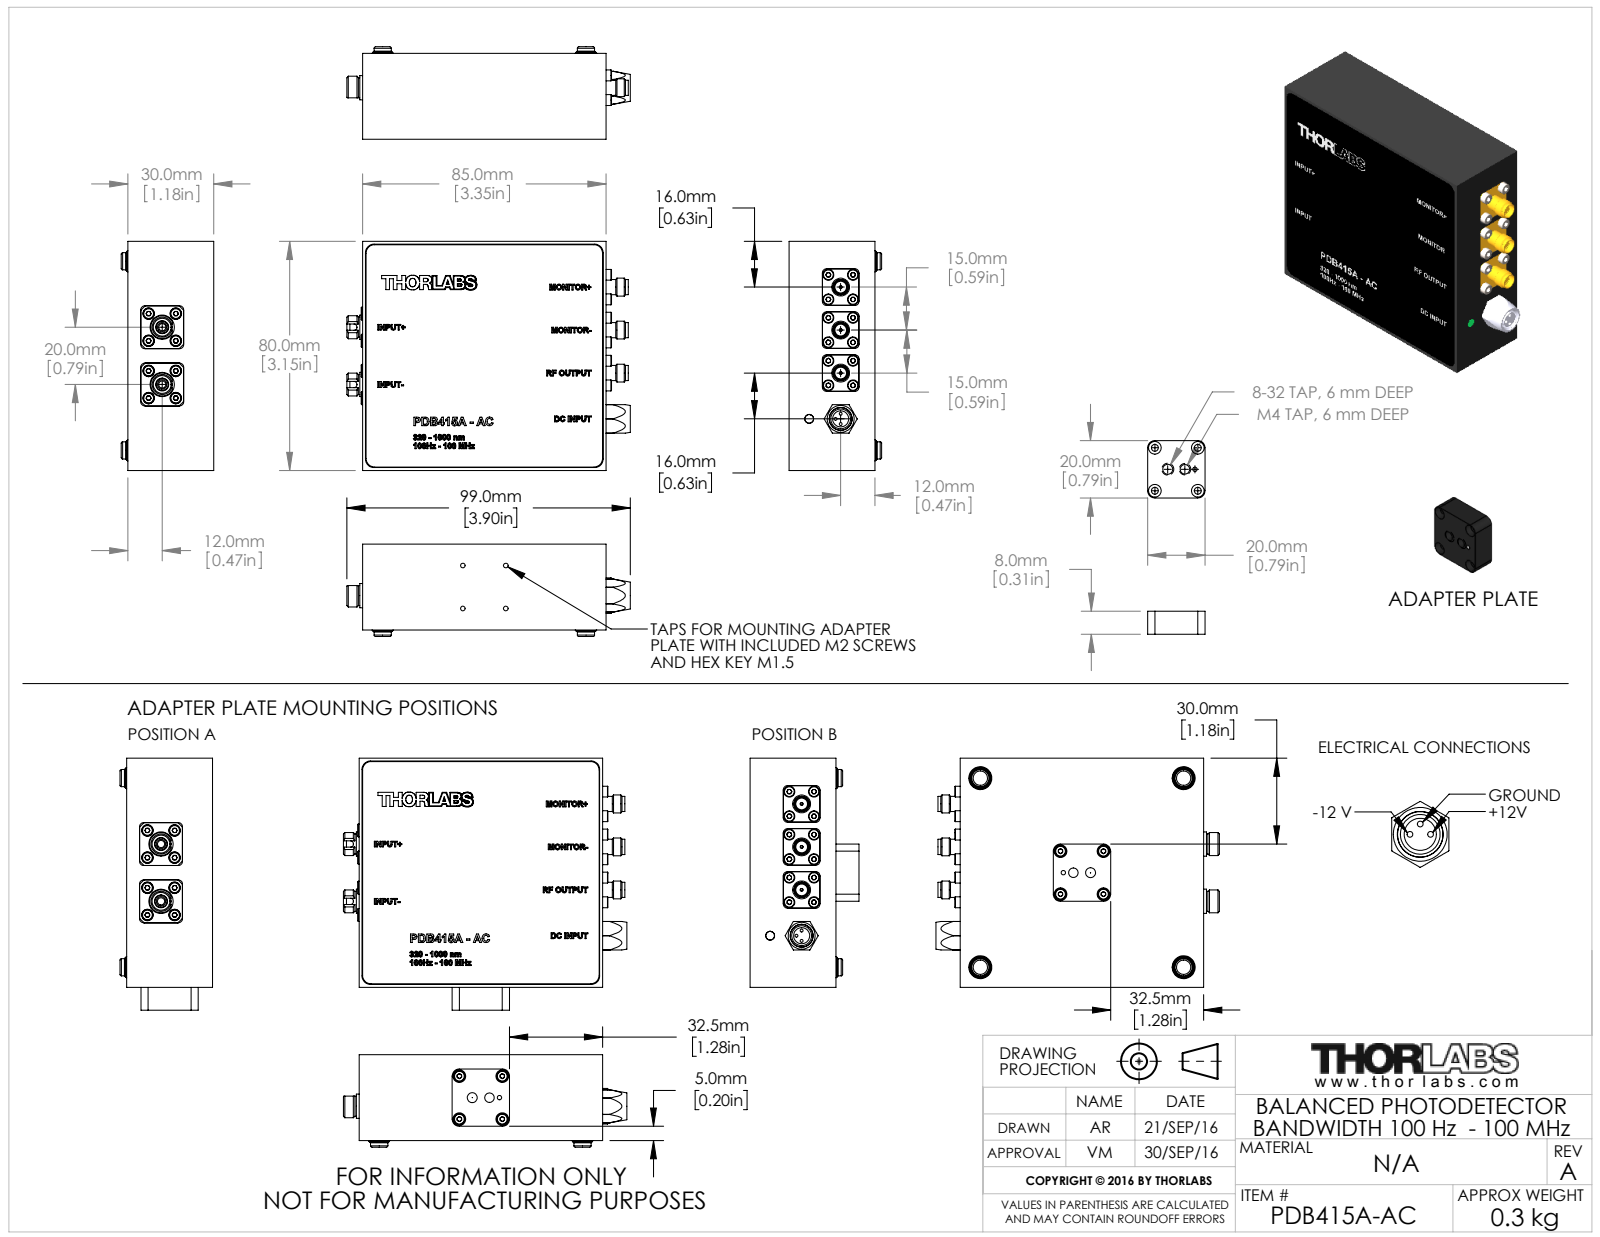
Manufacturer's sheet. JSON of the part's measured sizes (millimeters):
{"part_name": "MTN005470-E0W", "step_written_by": "SolidWorks 2014 (AUTOMOTIVE_DESIGN)", "units": "millimeters", "bodies": {"solids": 90, "faces": 3091, "planar": 1799, "cylindrical": 584, "other": 708}, "overall_size": [99, 88, 38], "volume_mm3": 87719, "surface_area_mm2": 57809, "round_holes": [[1.6, 38], [2.6, 12], [2.2, 8], [2.4, 8], [4, 8], [4.4, 8], [1.02, 6], [8, 5], [0.8, 3], [1, 3], [4.1, 3], [4.2, 3]], "round_bosses_or_shafts": [[3.8, 20], [2, 20], [4.5, 8], [2.5, 8], [0.43, 6], [6, 4], [6.22, 3], [5.3, 3]], "partial_cylinders_radius": [[1.5, 20], [3, 12], [2.5, 8], [5, 8], [1, 4], [9.5, 2], [5.75, 1]], "face_to_face_distances": [29.7, 6, 23.7, 5.5, 80, 2, 74.5, 85, 3.5, 83], "hole_center_spacings": [15, 6.08, 8.6, 9.5, 6.72, 8.75, 11.53, 12.9]}
